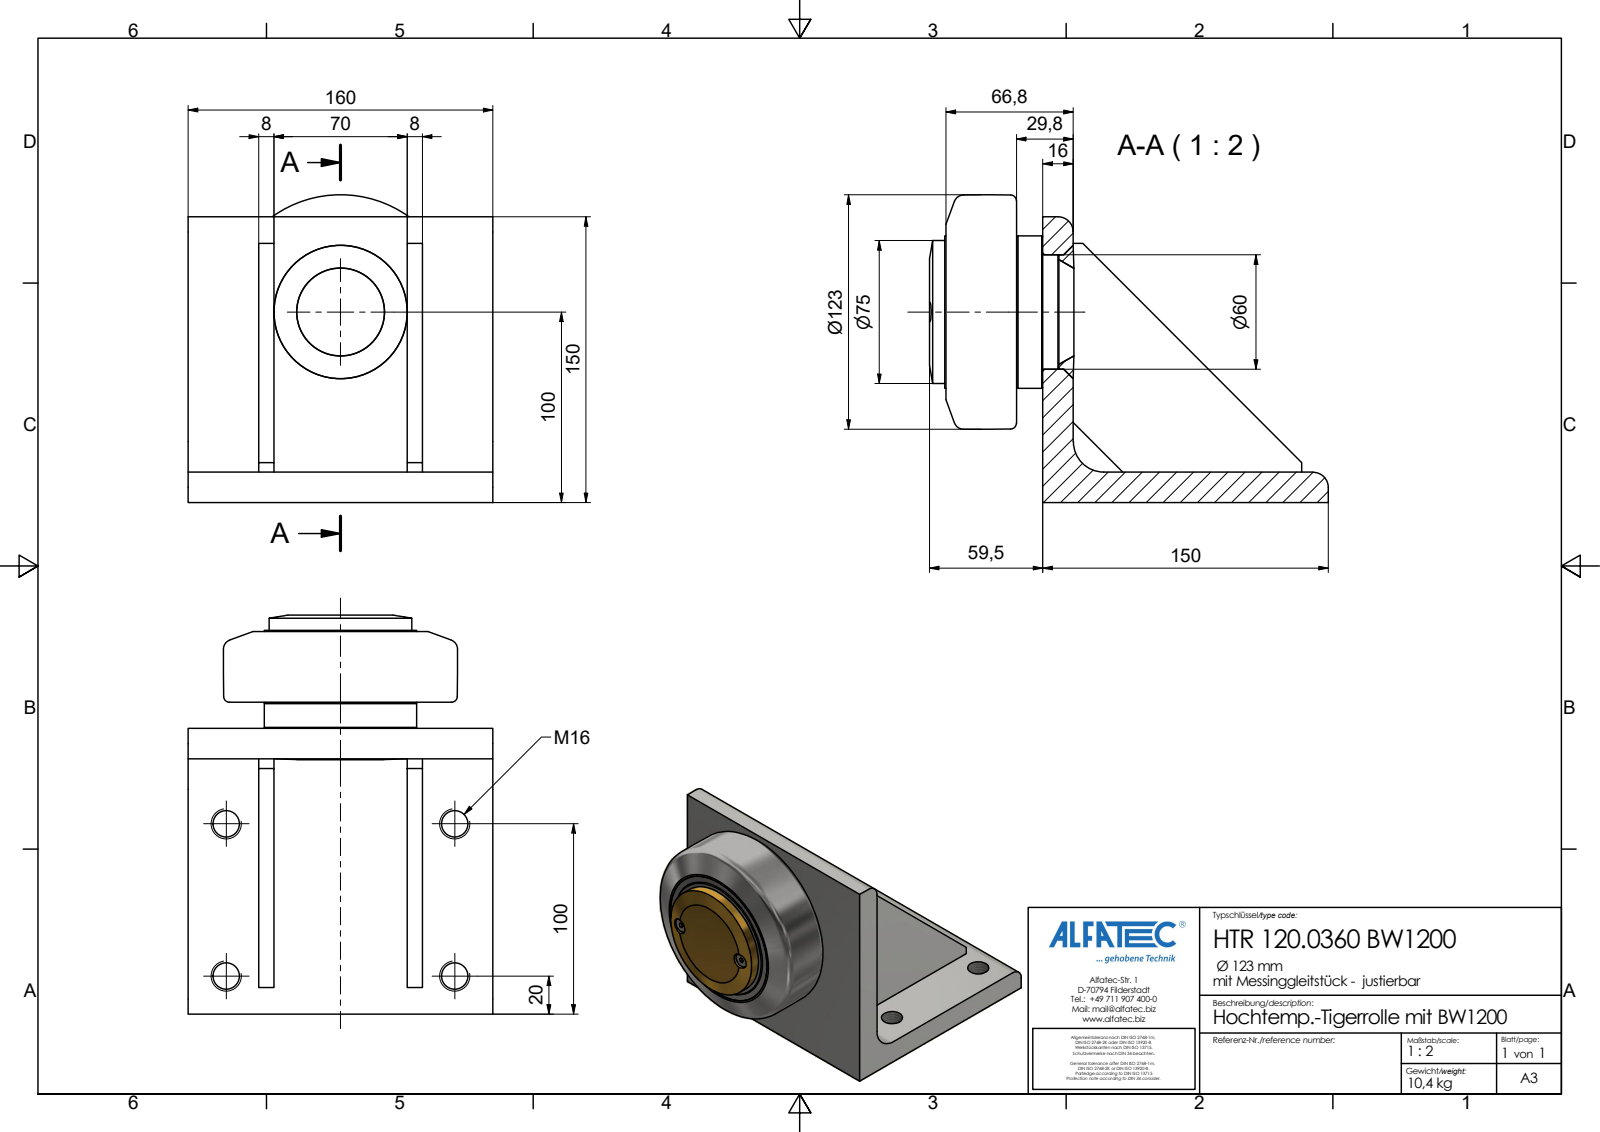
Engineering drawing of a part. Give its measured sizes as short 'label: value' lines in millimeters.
name: HTR 120.0360 BW1200_Kontur
written by: Autodesk Inventor 2020 (AP242_MANAGED_MODEL_BASED_3D_ENGINEERING_MIM_LF)
unit: mm
bodies: 1 solid, 67 faces (42 planar, 15 cylindrical, 10 other)
size: 209.5 × 161.5 × 160
volume: 1 370 000 mm³; area: 165 629 mm²
holes: 4× ⌀13.84, 2× ⌀10.4
bosses: 2× ⌀9.75, 1× ⌀80, 1× ⌀75
rounds: 2× R8, 1× R16
face distances: 16, 8, 78, 37, 45, 115, 123, 86, 70, 29.8
hole spacings: 80, 120, 144.22, 56
